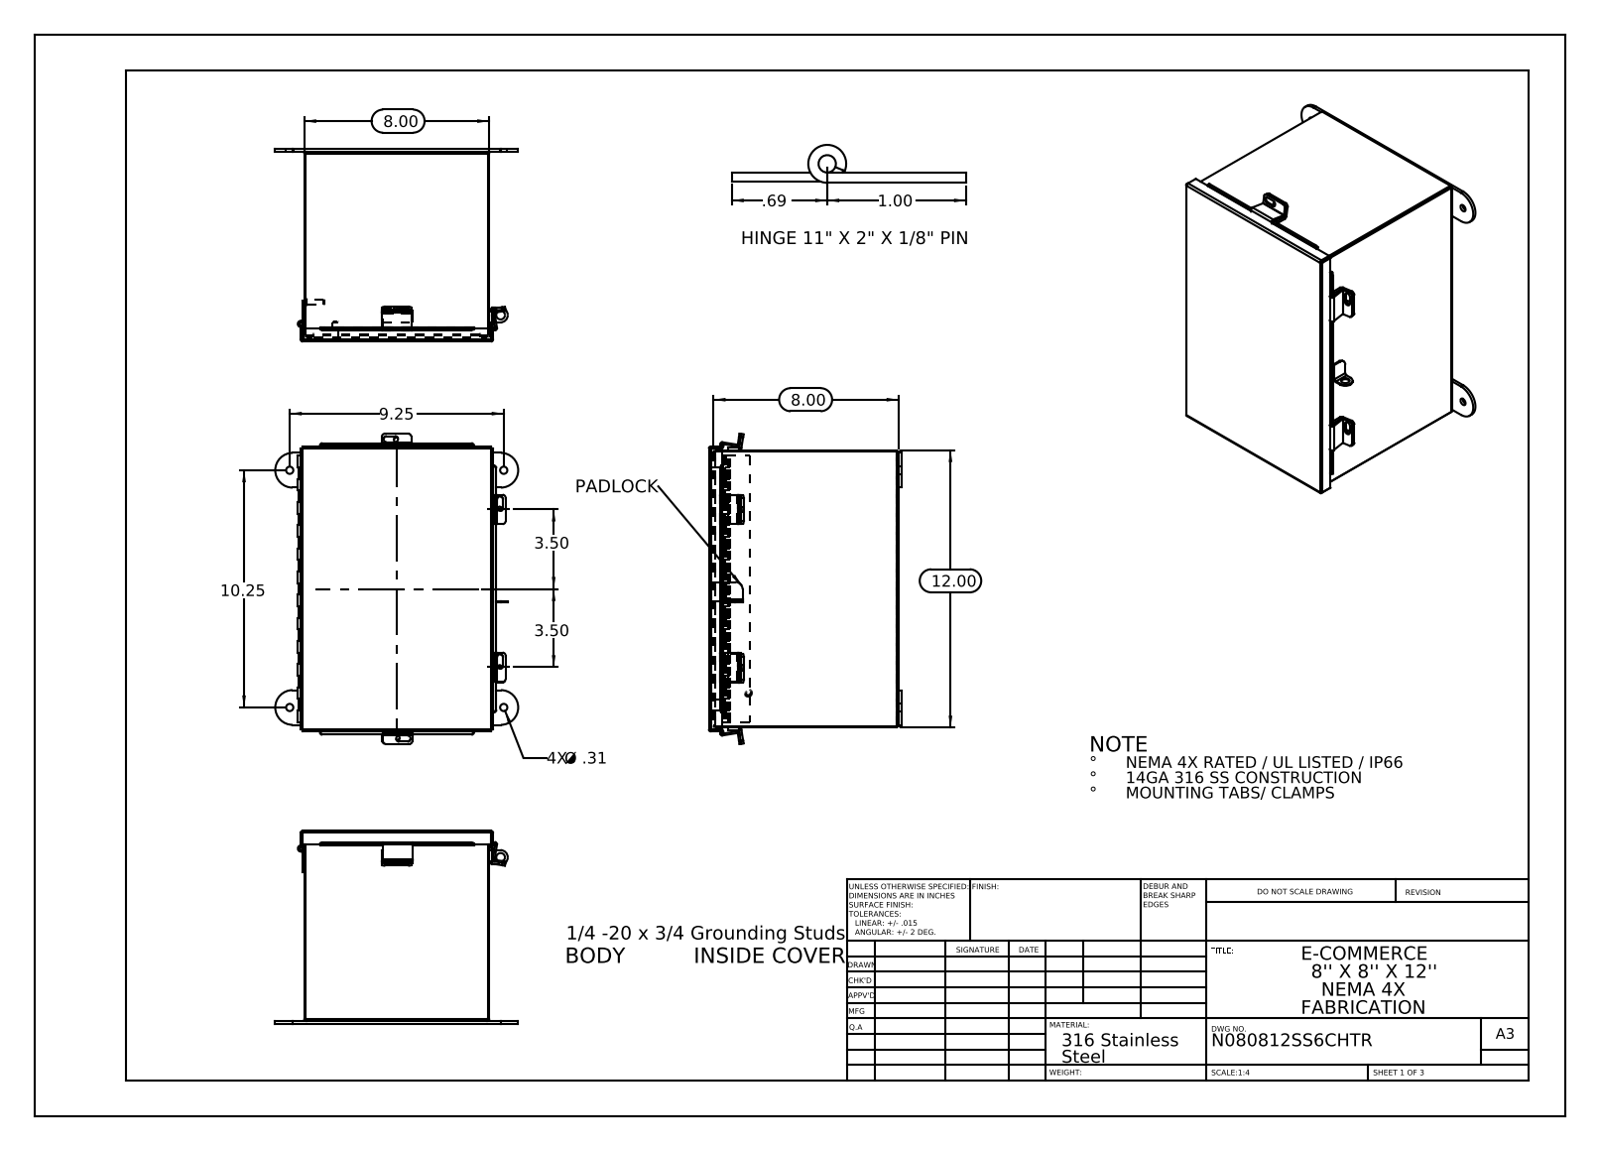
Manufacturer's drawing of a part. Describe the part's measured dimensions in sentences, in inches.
The part is named "N080812SSCHTR HW-CD-S-25020-034; N080812SSCHTR JIC_Cover_Template; N080812SSCHTR Hinge Cover Side JIC; N080812SSCHTR JIC Top (+8 more)". Its 3-D file was written by "SolidWorks 2013 (CONFIG_CONTROL_DESIGN)". It is 19 solids with 636 faces: 401 planar, 215 cylindrical and 20 other. Overall it measures 13.407 by 10.5 by 8.337 inches. Its volume is 47.42 cubic inches and its surface area 1 251 square inches. Round holes: 4 of diameter 0.25, 4 of diameter 0.313, 1 of diameter 0.125, 1 of diameter 0.125, 1 of diameter 0.375. Round bosses or shafts: 2 of diameter 0.315, 2 of diameter 0.236, 1 of diameter 0.273, 1 of diameter 0.25. Partial cylindrical surfaces (rounded edges, fillets, slot ends): 14 of radius 0.125, 12 of radius 0.009, 10 of radius 0.013, 10 of radius 0.088, 8 of radius 0.133, 6 of radius 0.083, 6 of radius 0.1, 4 of radius 0.75. The main face-to-face distances are 0.075, 7.925, 8.128, 11.925, 7.85, 8, 8.203, 8.053, 11.85, 12. The hole center spacings are 9.25, 10.25, 13.807, 6.85, 8.635.
